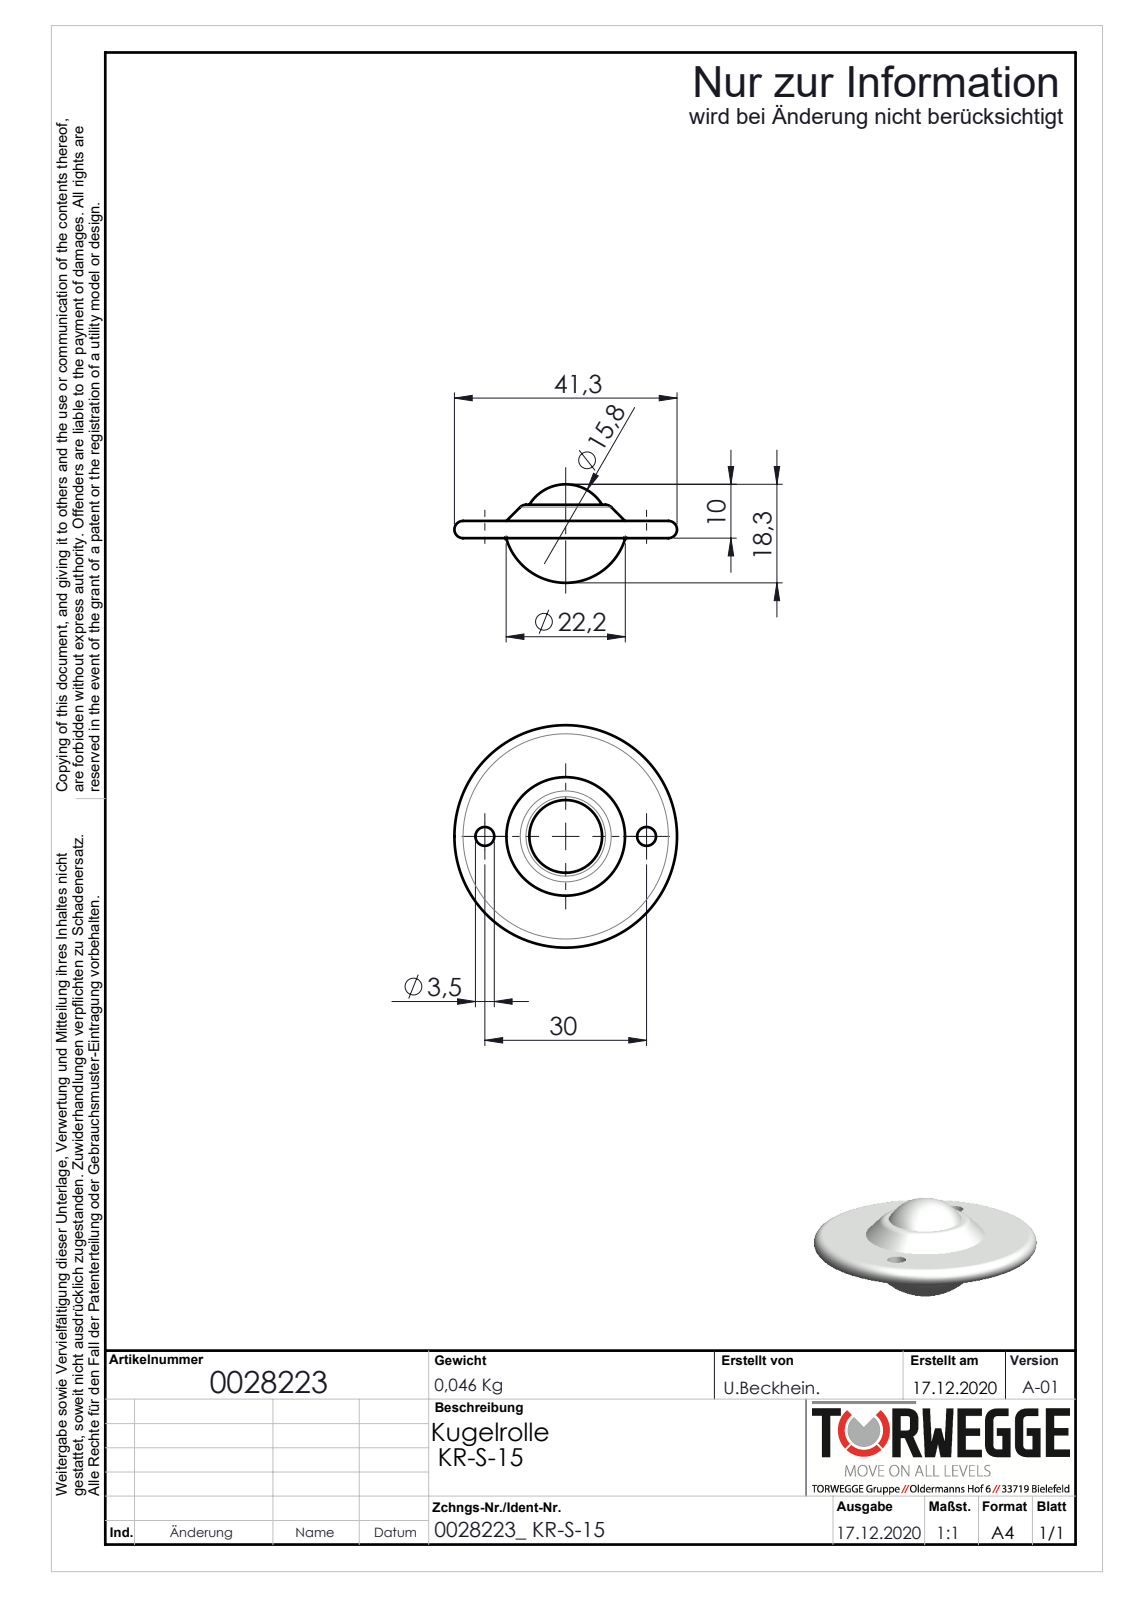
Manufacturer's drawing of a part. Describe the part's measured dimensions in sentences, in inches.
The part is named "0028223". Its 3-D file was written by "SolidWorks 2018 (AUTOMOTIVE_DESIGN)". It is 1 solid with 23 faces: 4 planar, 6 cylindrical and 13 other. Overall it measures 1.626 by 1.626 by 0.709 inches. Its volume is 0.397 cubic inches and its surface area 5.284 square inches. Round holes: 2 of diameter 0.138, 1 of diameter 1.437. The main face-to-face distances are 0.087, 0.039, 0.126, 0.244, 0.205, 0.118. The hole center spacings are 0.591, 1.181.
